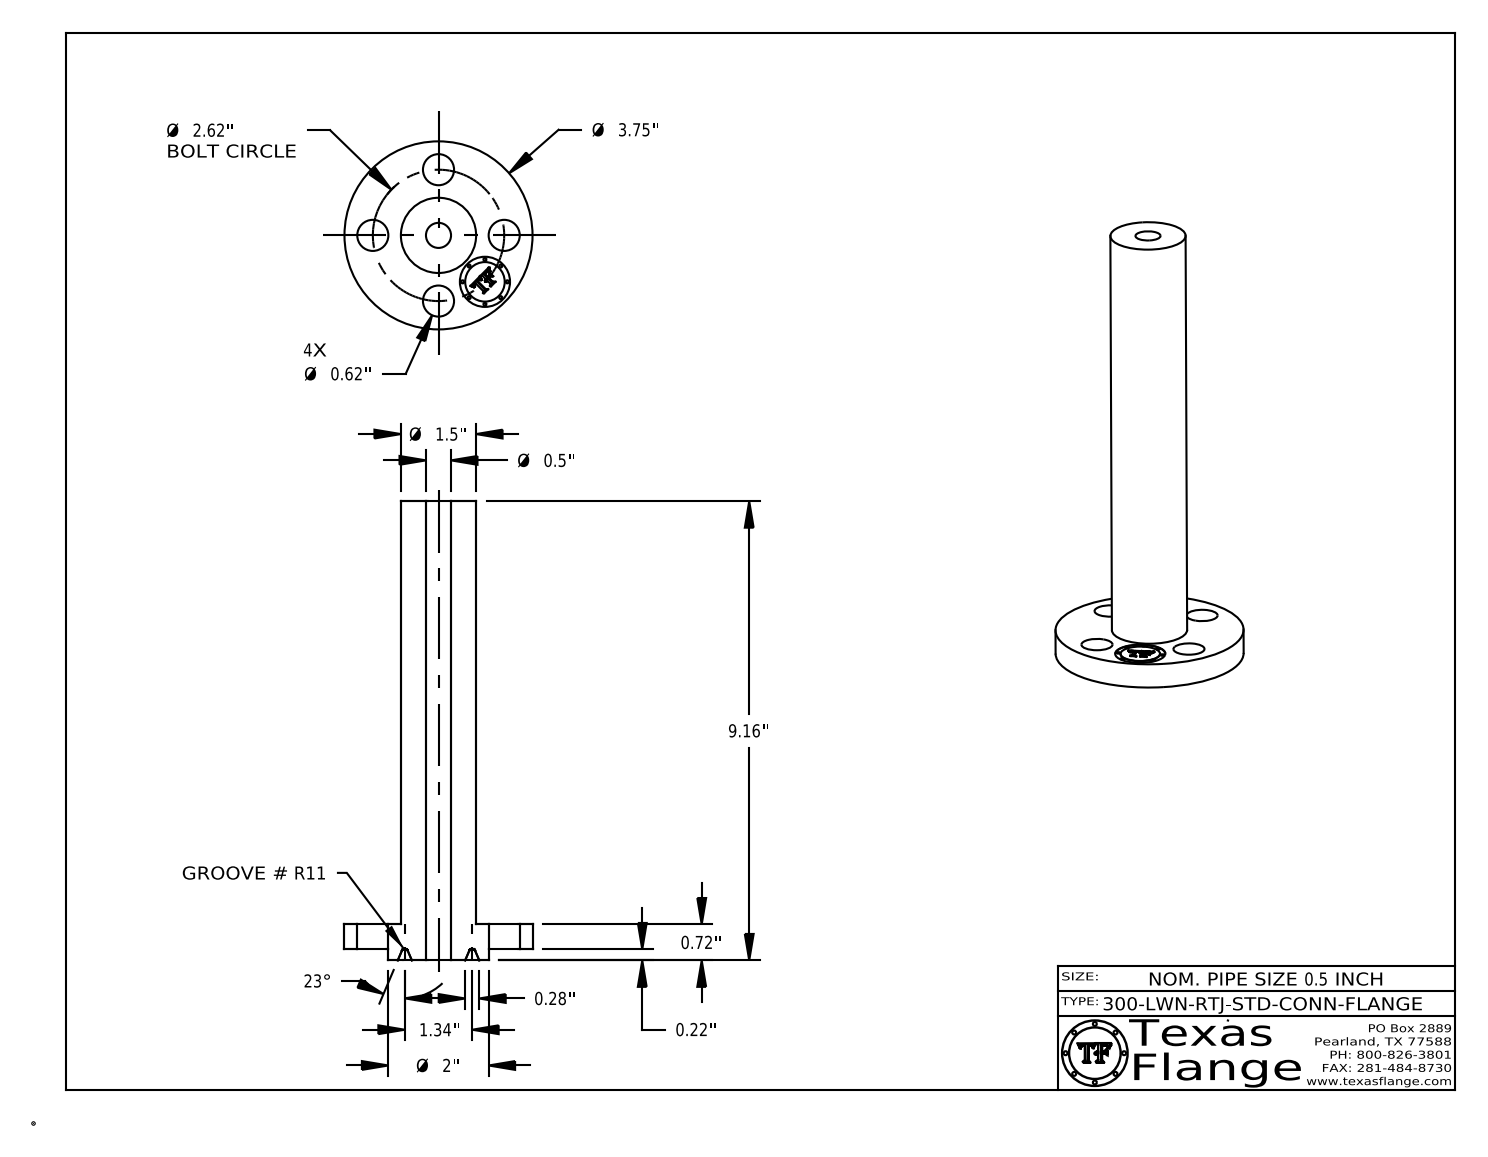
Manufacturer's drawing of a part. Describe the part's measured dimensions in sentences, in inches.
The part is named "0.5-300-LWN-RTJ-STD-CONN-FLANGE". Its 3-D file was written by "CATIA V5 STEP AP214 (AUTOMOTIVE_DESIGN)". It is 1 solid with 415 faces: 371 planar, 36 cylindrical and 8 other. Overall it measures 9.156 by 3.75 by 3.75 inches. Its volume is 18.52 cubic inches and its surface area 85.8 square inches. Round holes: 4 of diameter 0.62, 1 of diameter 0.5, 1 of diameter 1. Round bosses or shafts: 8 of diameter 0.061, 1 of diameter 3.75, 1 of diameter 2, 1 of diameter 1.5, 1 of diameter 0.788. The main face-to-face distances are 0.498, 0.219, 0.717, 9.156, 8.937, 8.44, 0.711, 0.493, 8.445, 0.298. The hole center spacings are 1.31, 1.852, 1.003, 2.42, 2.62, 1.31.
